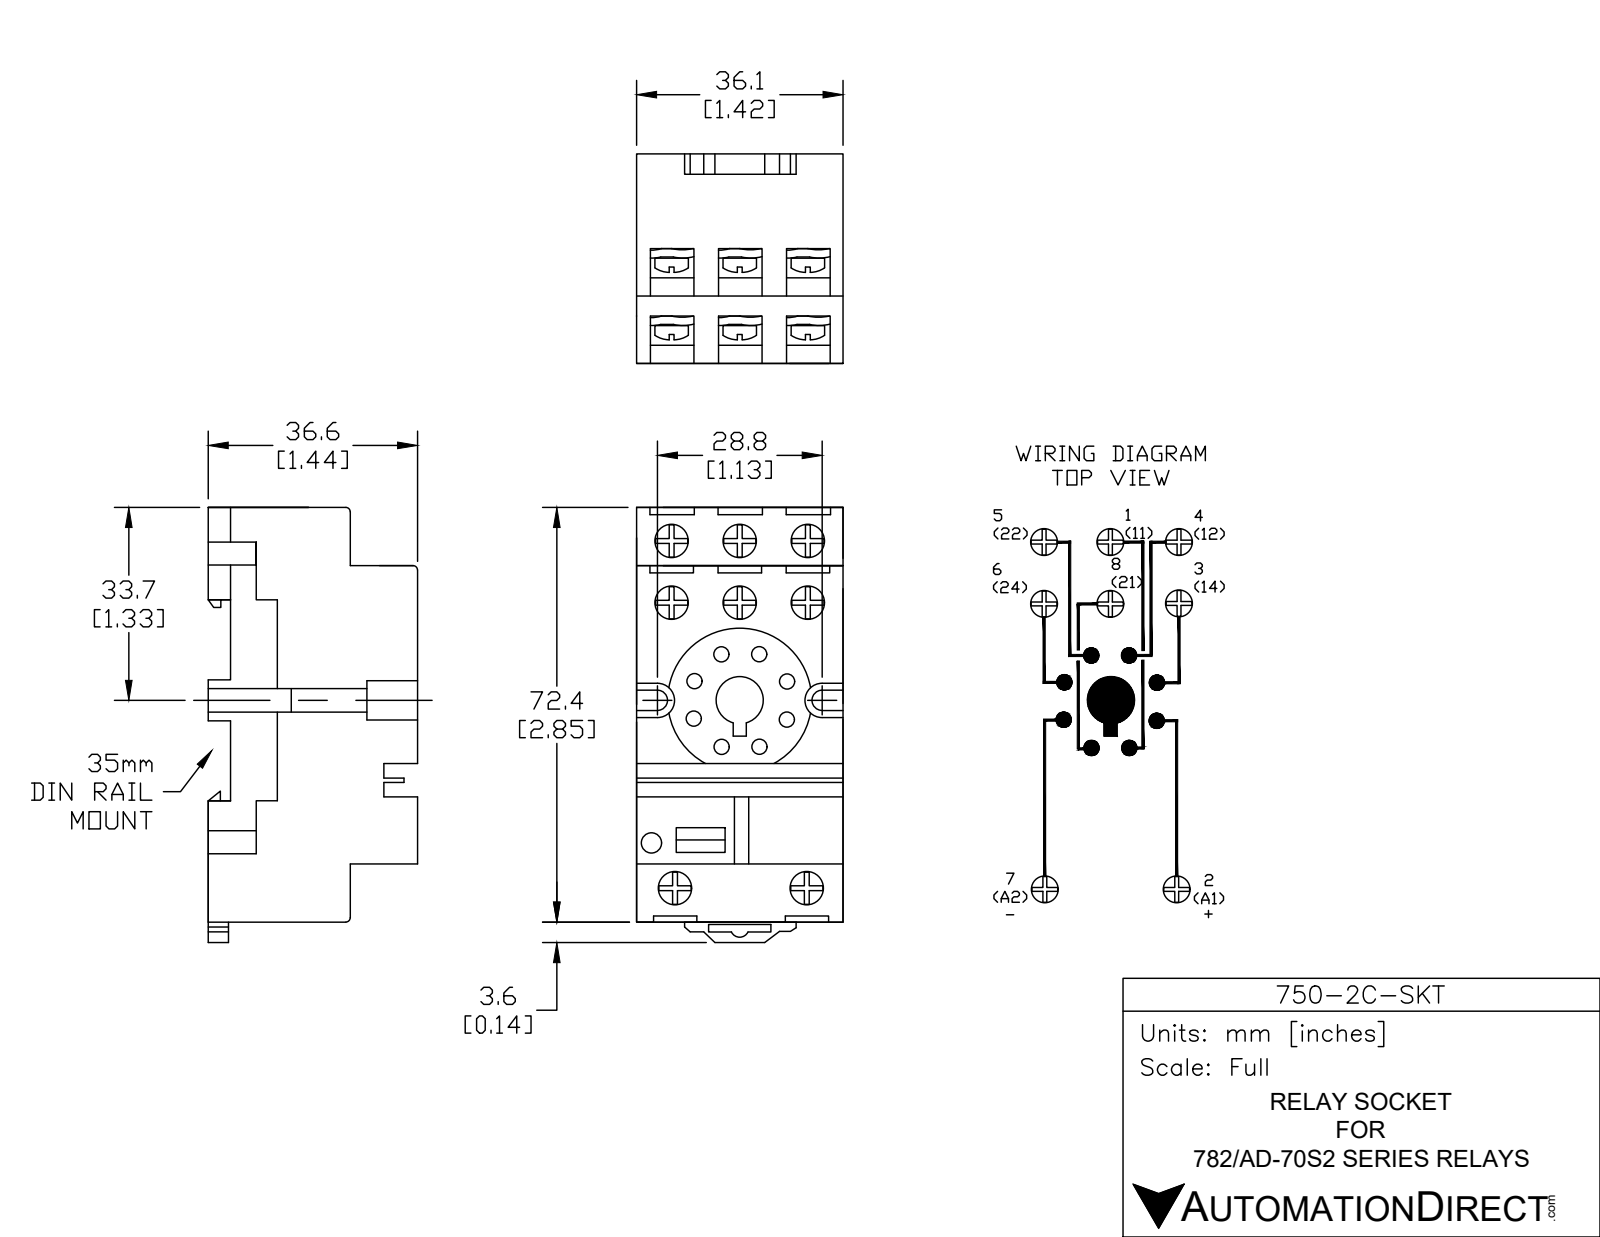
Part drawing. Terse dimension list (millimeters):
name: 750-2C-SKT
written by: SolidWorks 2013 (AUTOMOTIVE_DESIGN)
unit: mm
bodies: 1 solid, 397 faces (303 planar, 94 cylindrical, 0 other)
size: 76.7 × 36.6 × 36.1
volume: 75 760 mm³; area: 17 010 mm²
holes: 8× ⌀2.7, 8× ⌀5.3, 1× ⌀3.2, 1× ⌀8.2
rounds: 36× R0.4, 2× R1.5, 2× R1.8, 2× R3.4, 1× R3.6, 1× R12.5
face distances: 36.1, 3.9, 36.6, 32.7, 10.2, 11.8, 71.6, 61.5, 24.8, 20.9
hole spacings: 8.6, 12.2, 16, 6.6, 6.6, 10.2, 11.9, 11.9
